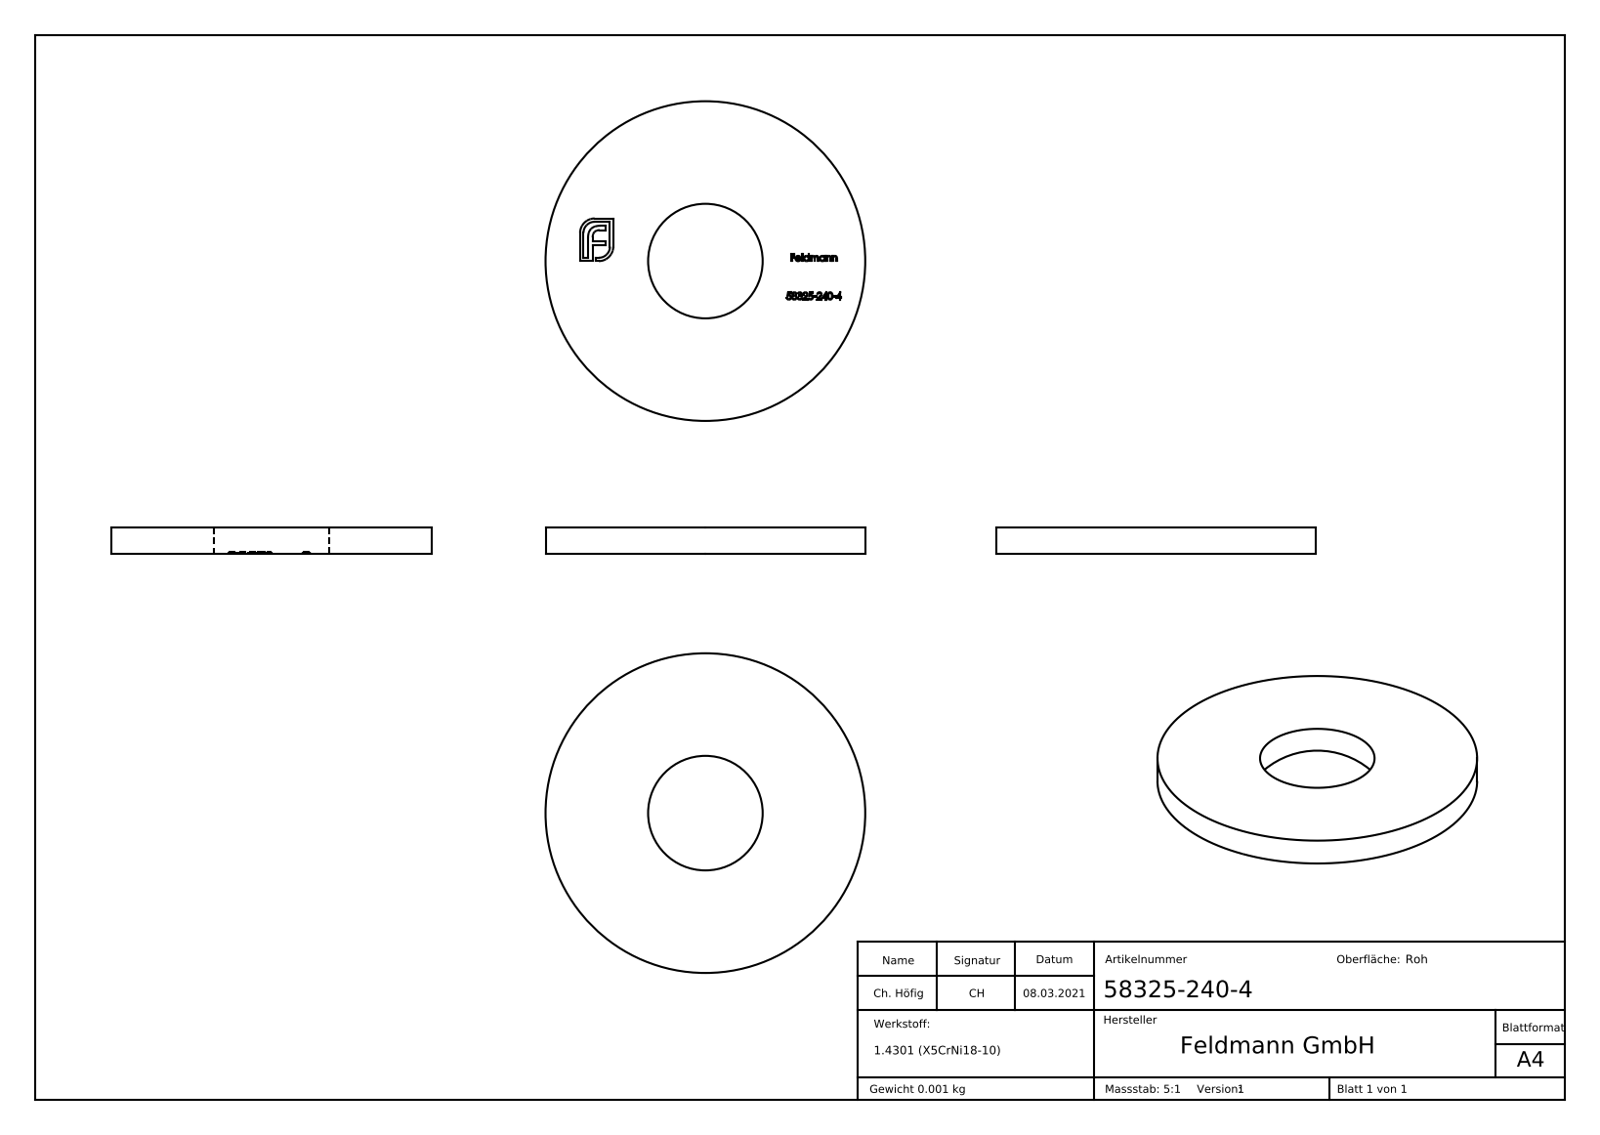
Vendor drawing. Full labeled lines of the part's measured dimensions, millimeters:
Part name (STEP PRODUCT): 58325-240-4
STEP written by: SolidWorks 2018 (CONFIG_CONTROL_DESIGN)
Units: millimetres
Bodies: 1 solid, 305 faces (165 planar, 4 cylindrical, 136 other)
Overall size (bounding box): 12 × 12 × 1
Volume: 98 mm³ · Surface area: 252 mm²
Round holes (diameter × count): ⌀4.3 ×1
Round bosses / shafts (diameter × count): ⌀12 ×1
Main face-to-face distances: 1, 0.9, 1.12, 0.65, 1.47, 1.24, 0.82, 0.58, 1.44, 1.6
